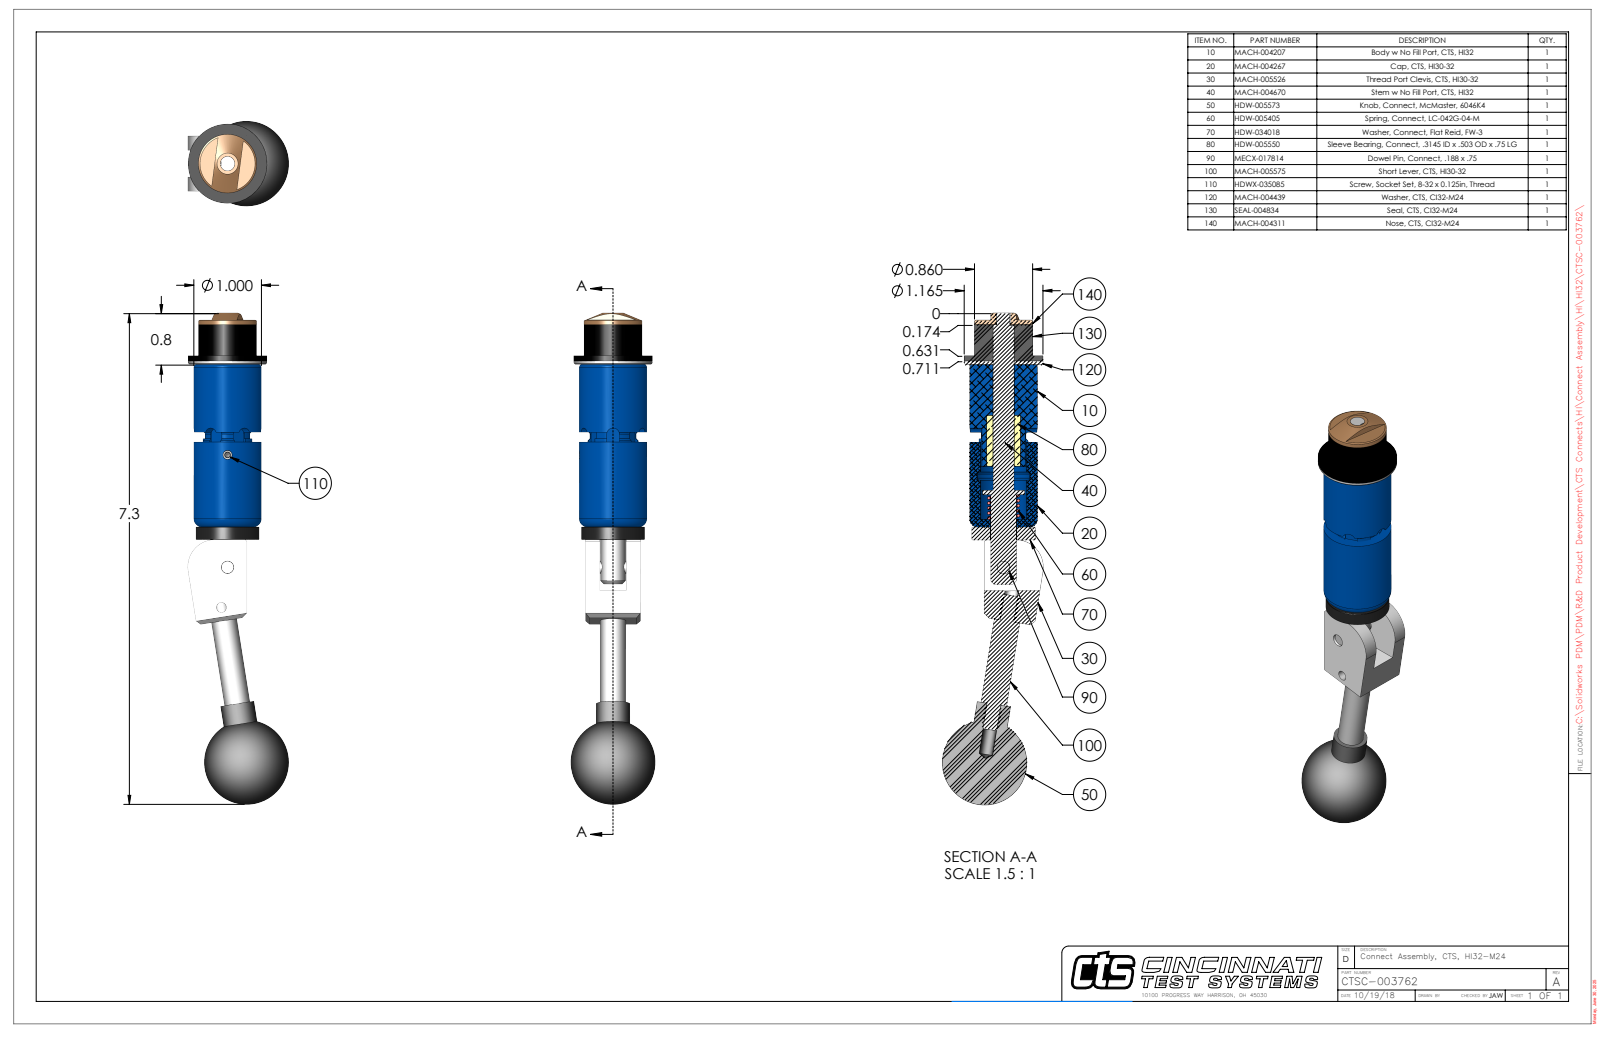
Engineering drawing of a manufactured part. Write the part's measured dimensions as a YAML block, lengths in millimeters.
part_name: "CTSC-003762"
step_written_by: "SolidWorks 2023 (AUTOMOTIVE_DESIGN)"
units: millimeters
bodies: {solids: 9, faces: 268, planar: 100, cylindrical: 110, other: 58}
overall_size: [184.3, 37.9, 31.8]
volume: 68870
surface_area: 23550
round_holes:
  - {diameter: 5.1, count: 2}
  - {diameter: 3.5, count: 1}
  - {diameter: 3.8, count: 1}
  - {diameter: 4.8, count: 1}
  - {diameter: 5.4, count: 1}
  - {diameter: 7.9, count: 1}
  - {diameter: 8, count: 1}
  - {diameter: 8, count: 1}
  - {diameter: 9.8, count: 1}
  - {diameter: 10, count: 1}
  - {diameter: 17.5, count: 1}
round_bosses_or_shafts:
  - {diameter: 6.4, count: 2}
  - {diameter: 5.1, count: 2}
  - {diameter: 29.6, count: 1}
  - {diameter: 25.4, count: 1}
  - {diameter: 23.8, count: 1}
  - {diameter: 21.8, count: 1}
  - {diameter: 12.7, count: 1}
  - {diameter: 9.7, count: 1}
partial_cylinders:
  - {radius: 2.4, count: 6}
  - {radius: 0.7, count: 2}
  - {radius: 9.5, count: 1}
  - {radius: 10.2, count: 1}
  - {radius: 11.8, count: 1}
face_to_face_distances: [1.3, 5.3, 15.3, 13.6, 14.9, 75.8, 62.2, 60.9, 20.6, 80.6]
hole_center_spacings: [15.2, 42.1, 57.2]
